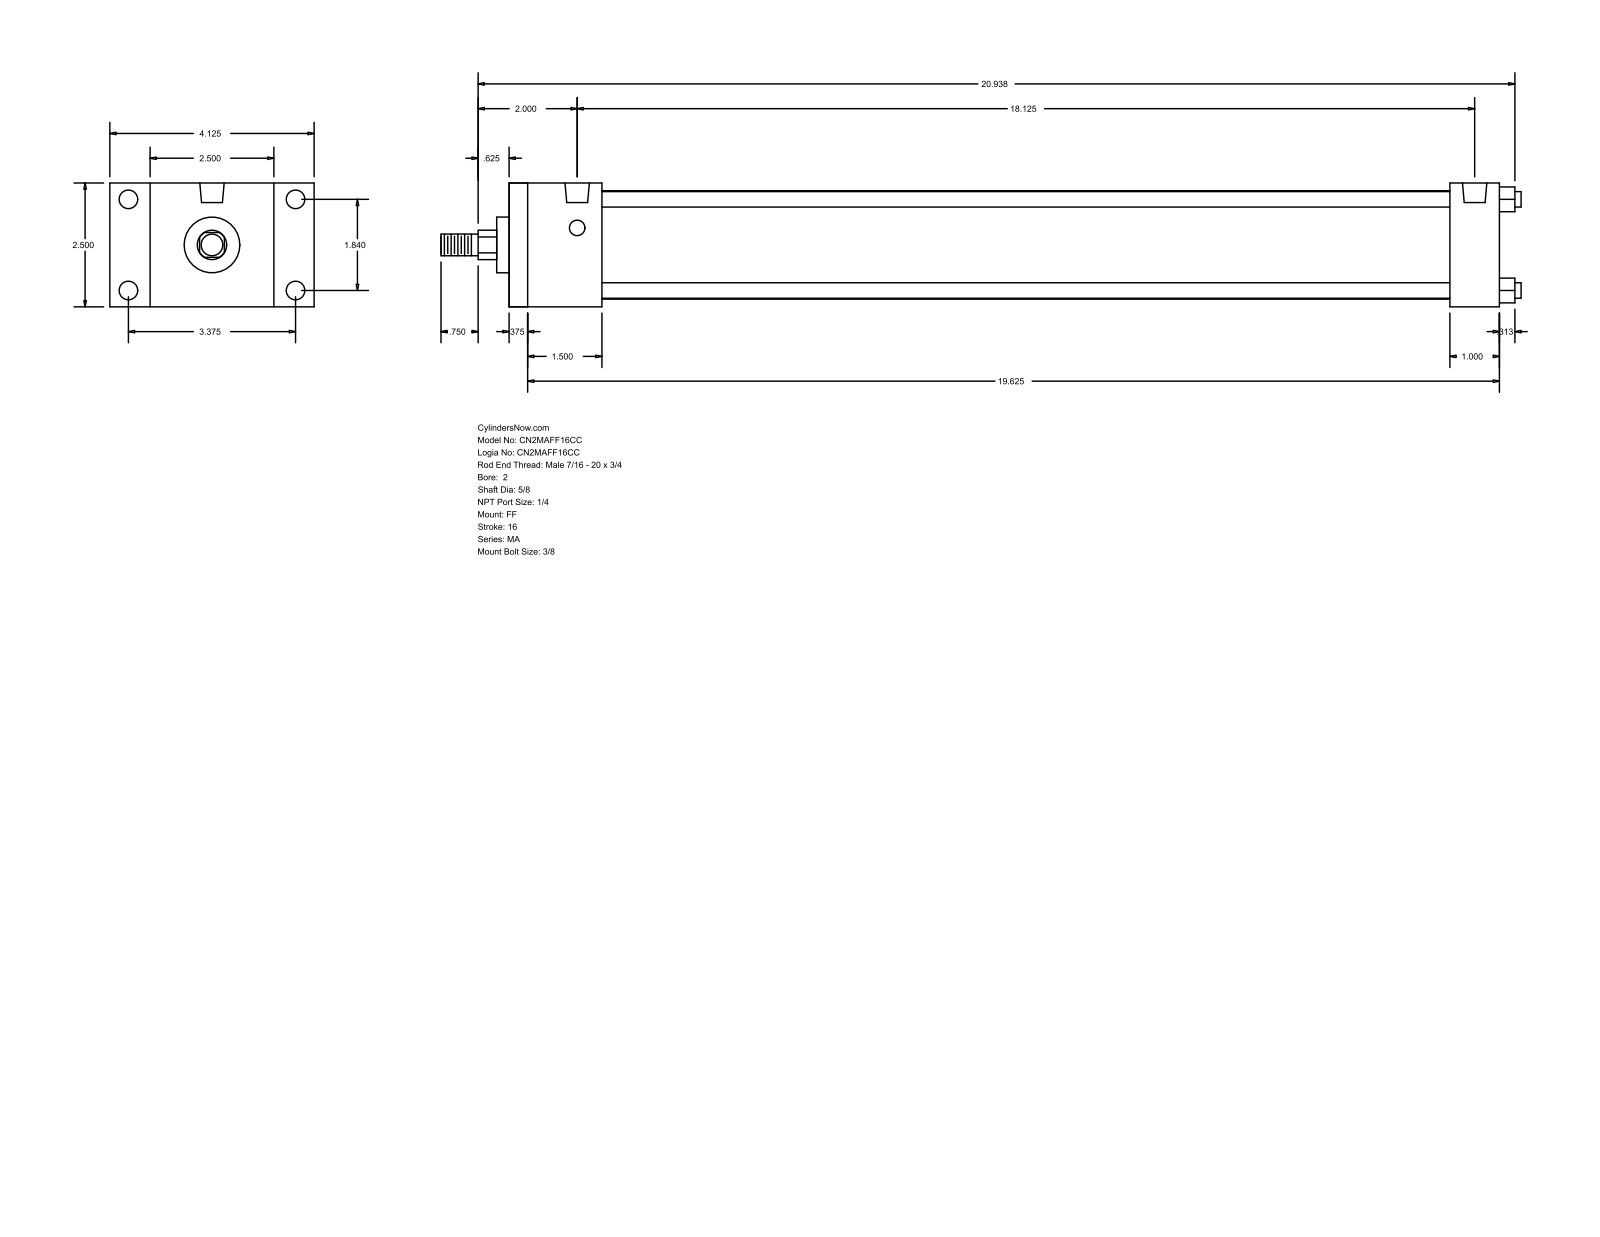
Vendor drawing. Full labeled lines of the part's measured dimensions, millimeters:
Part name (STEP PRODUCT): MA_FF__0200_0.625
STEP written by: GSSL Pune (CONFIG_CONTROL_DESIGN)
Units: millimetres
Bodies: 0 solids, 92 faces (64 planar, 28 cylindrical, 0 other)
Overall size (bounding box): 554.04 × 104.78 × 63.5
Round holes (diameter × count): ⌀7.94 ×4, ⌀9.53 ×4, ⌀12.49 ×2
Round bosses / shafts (diameter × count): ⌀7.94 ×4, ⌀55.63 ×1, ⌀28.57 ×1, ⌀15.88 ×1, ⌀11.11 ×1
Partial cylindrical surfaces — rounded edges, fillets, slot ends (radius × count): R7.54 ×1
Main face-to-face distances: 63.5, 508, 498.48, 9.52, 25.4, 38.1, 47.62, 482.6, 473.08, 434.98
Hole centre spacings: 46.74, 85.72, 97.63, 460.38
